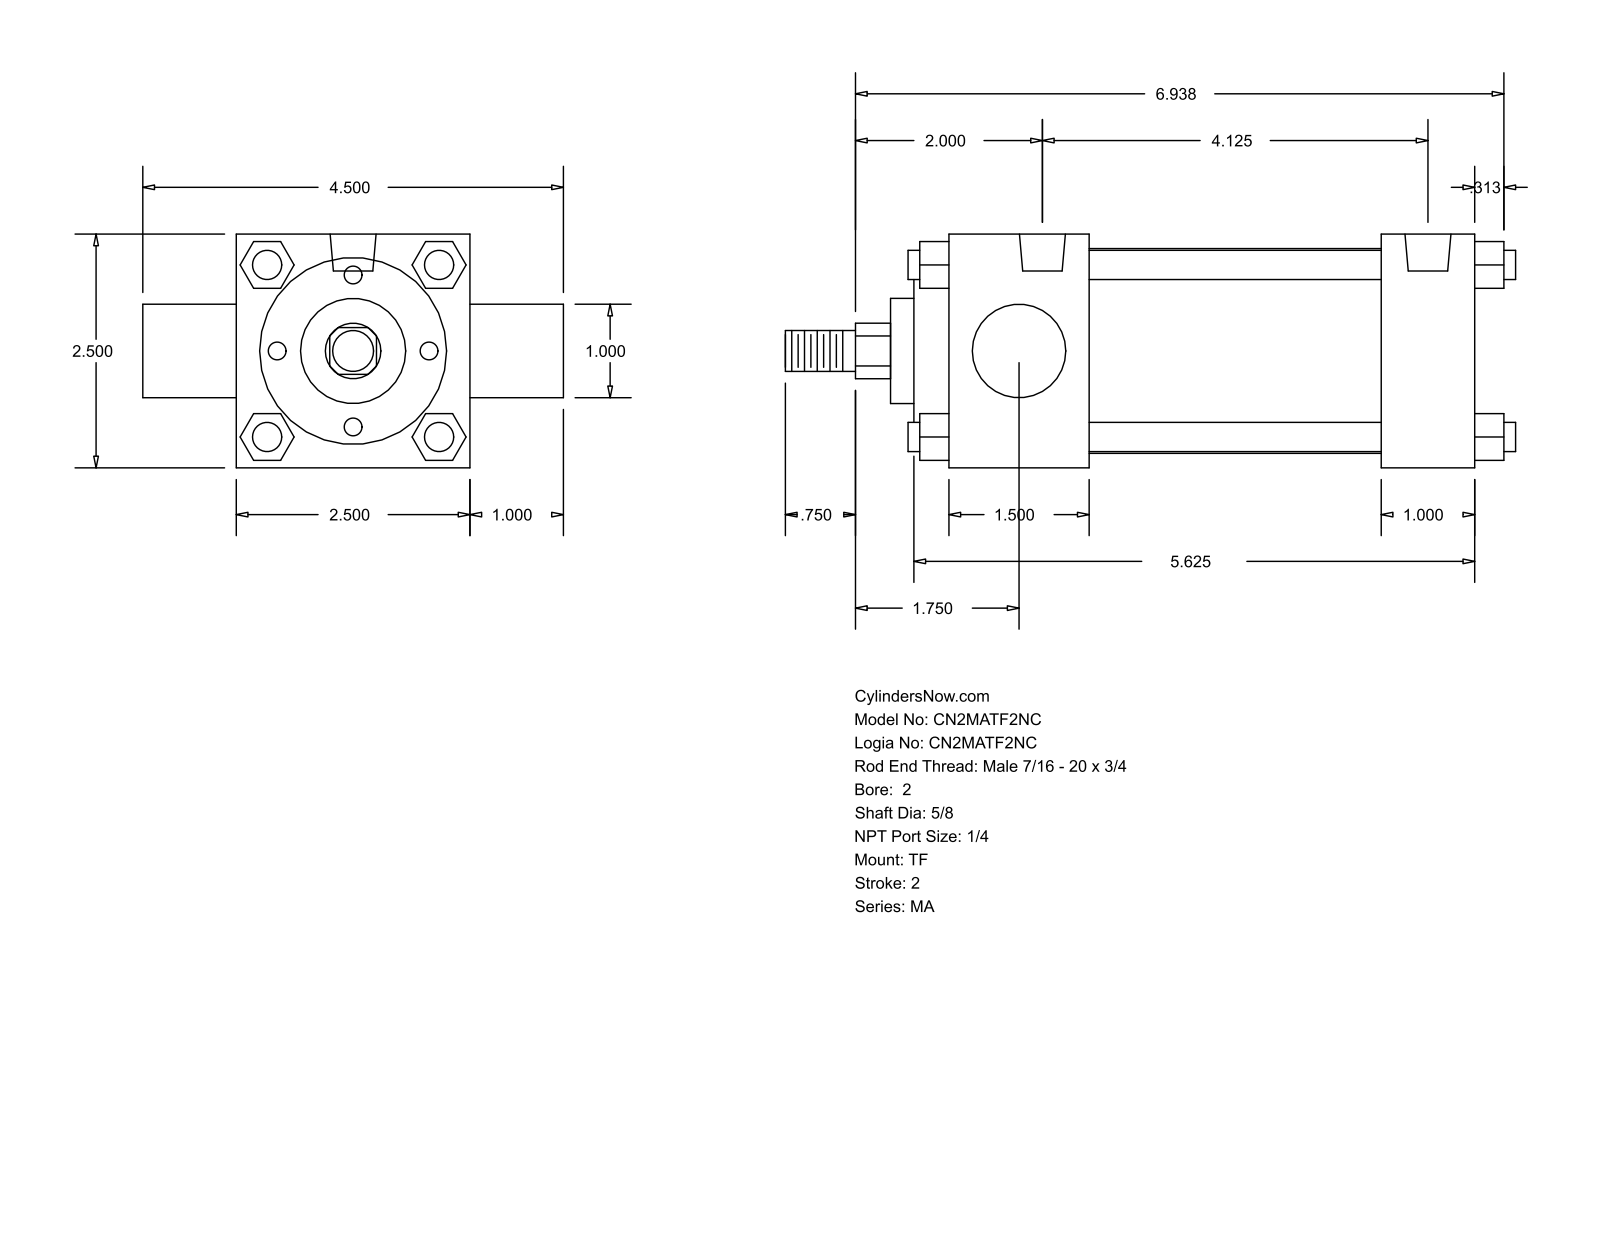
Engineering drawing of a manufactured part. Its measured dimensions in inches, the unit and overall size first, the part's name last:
Units: inches
Overall size (bounding box): 7.813 × 4.5 × 2.5
Round holes (diameter × count): ⌀0.313 ×3, ⌀0.492 ×2
Round bosses / shafts (diameter × count): ⌀0.313 ×4, ⌀2.19 ×1, ⌀2 ×1, ⌀1.125 ×1, ⌀1 ×1, ⌀0.625 ×1, ⌀0.437 ×1
Partial cylindrical surfaces — rounded edges, fillets, slot ends (radius × count): R0.297 ×1
Main face-to-face distances: 2.5, 1, 1.5, 5.625, 0.5, 4.625, 3.125, 4.125, 0.375, 1.875
Hole centre spacings: 4.125
Bodies: 0 solids, 122 faces (93 planar, 29 cylindrical, 0 other)
Part name (STEP PRODUCT): MA_TF__0200_0.625
STEP written by: GSSL Pune (CONFIG_CONTROL_DESIGN)
